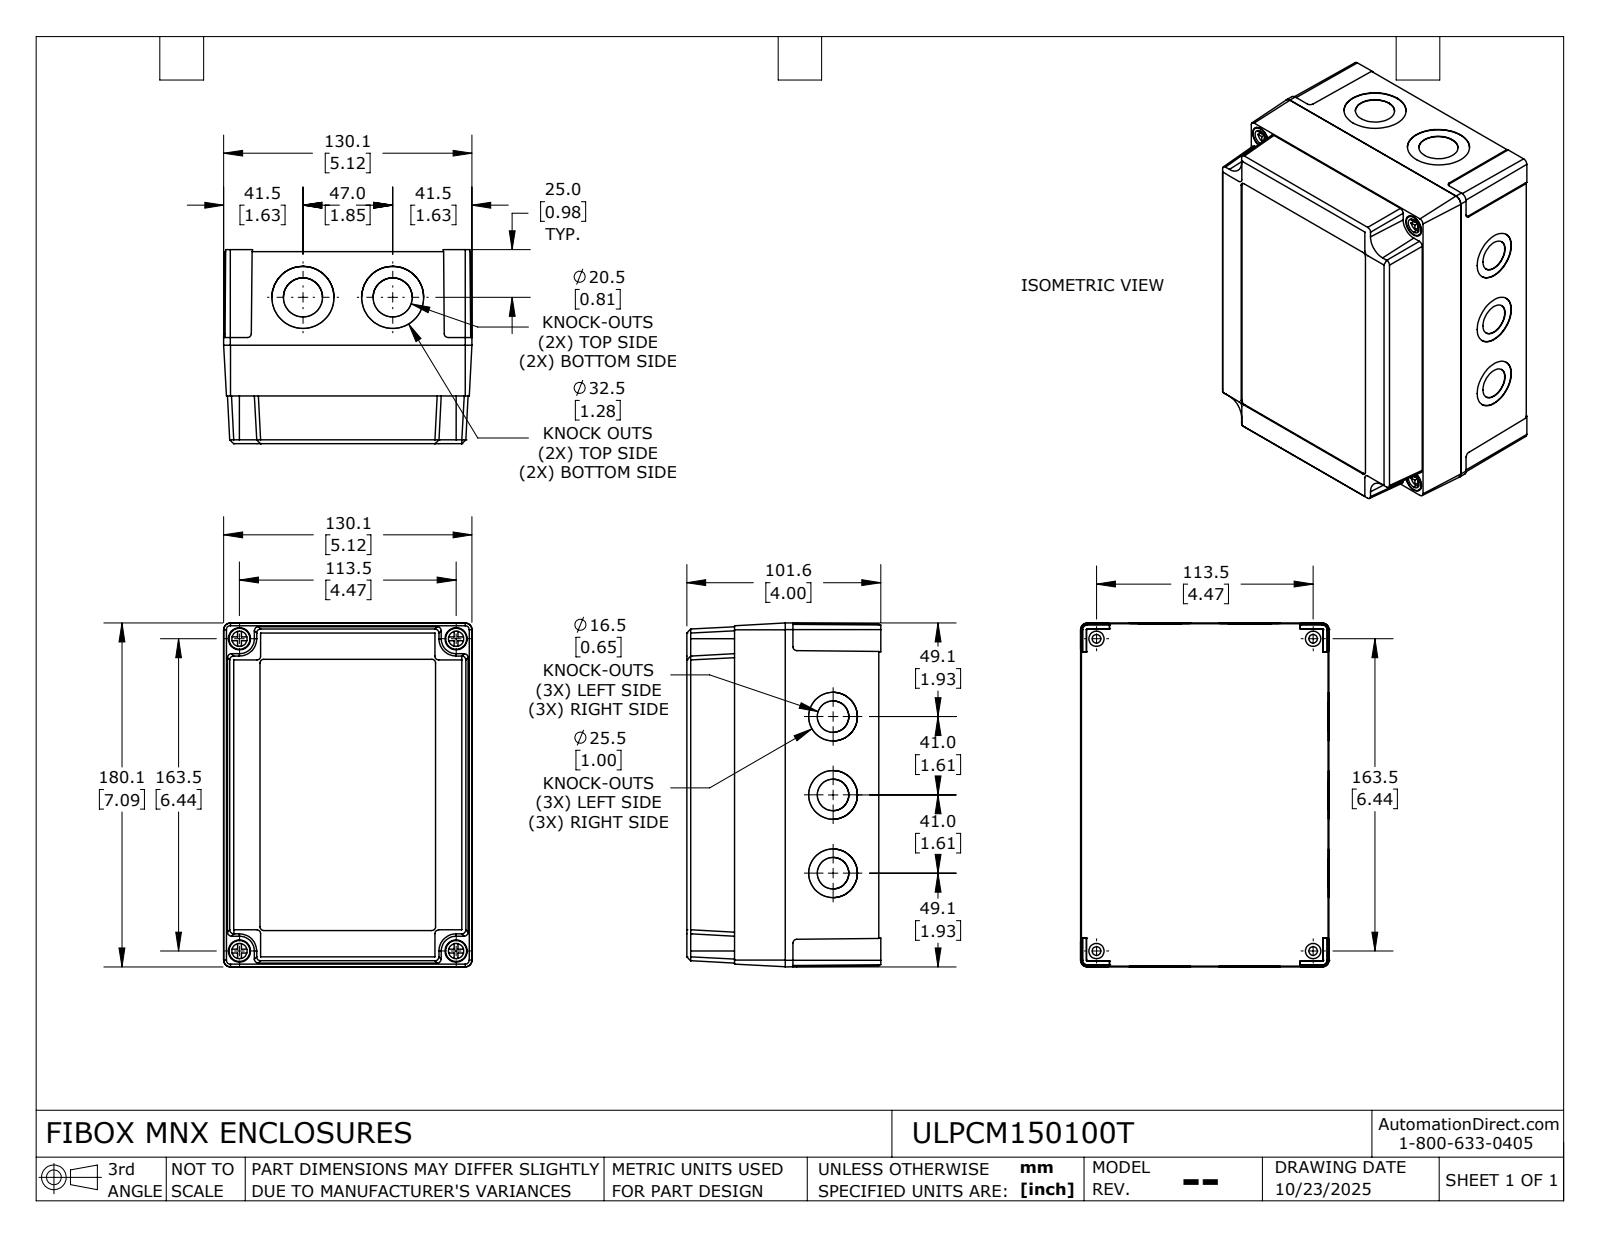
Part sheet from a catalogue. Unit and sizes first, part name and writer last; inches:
Units: inches
Overall size (bounding box): 7.091 × 5.122 × 4
Round holes (diameter × count): ⌀0.126 ×8, ⌀0.157 ×8, ⌀0.65 ×6, ⌀1.004 ×6, ⌀0.177 ×4, ⌀0.315 ×4, ⌀0.457 ×4, ⌀0.807 ×4, ⌀1.28 ×4
Round bosses / shafts (diameter × count): ⌀0.315 ×8, ⌀0.098 ×8, ⌀0.433 ×4, ⌀0.283 ×4
Partial cylindrical surfaces — rounded edges, fillets, slot ends (radius × count): R0.079 ×8, R0.083 ×8, R0.056 ×6, R0.021 ×4, R0.197 ×4, R0.023 ×2
Main face-to-face distances: 3.862, 0.118, 3.744, 0.165, 0.079, 3.823, 3.941, 0.055, 0.078, 0.098
Hole centre spacings: 1.333, 1.614, 1.939, 1.969, 2.281, 3.252, 3.276, 4.054
Volume: 19.99 in³ · Surface area: 344 in²
Bodies: 6 solids, 581 faces (335 planar, 200 cylindrical, 46 other)
Part name (STEP PRODUCT): ULPCM150100T_Default
STEP written by: SolidWorks 2024 (CONFIG_CONTROL_DESIGN)
